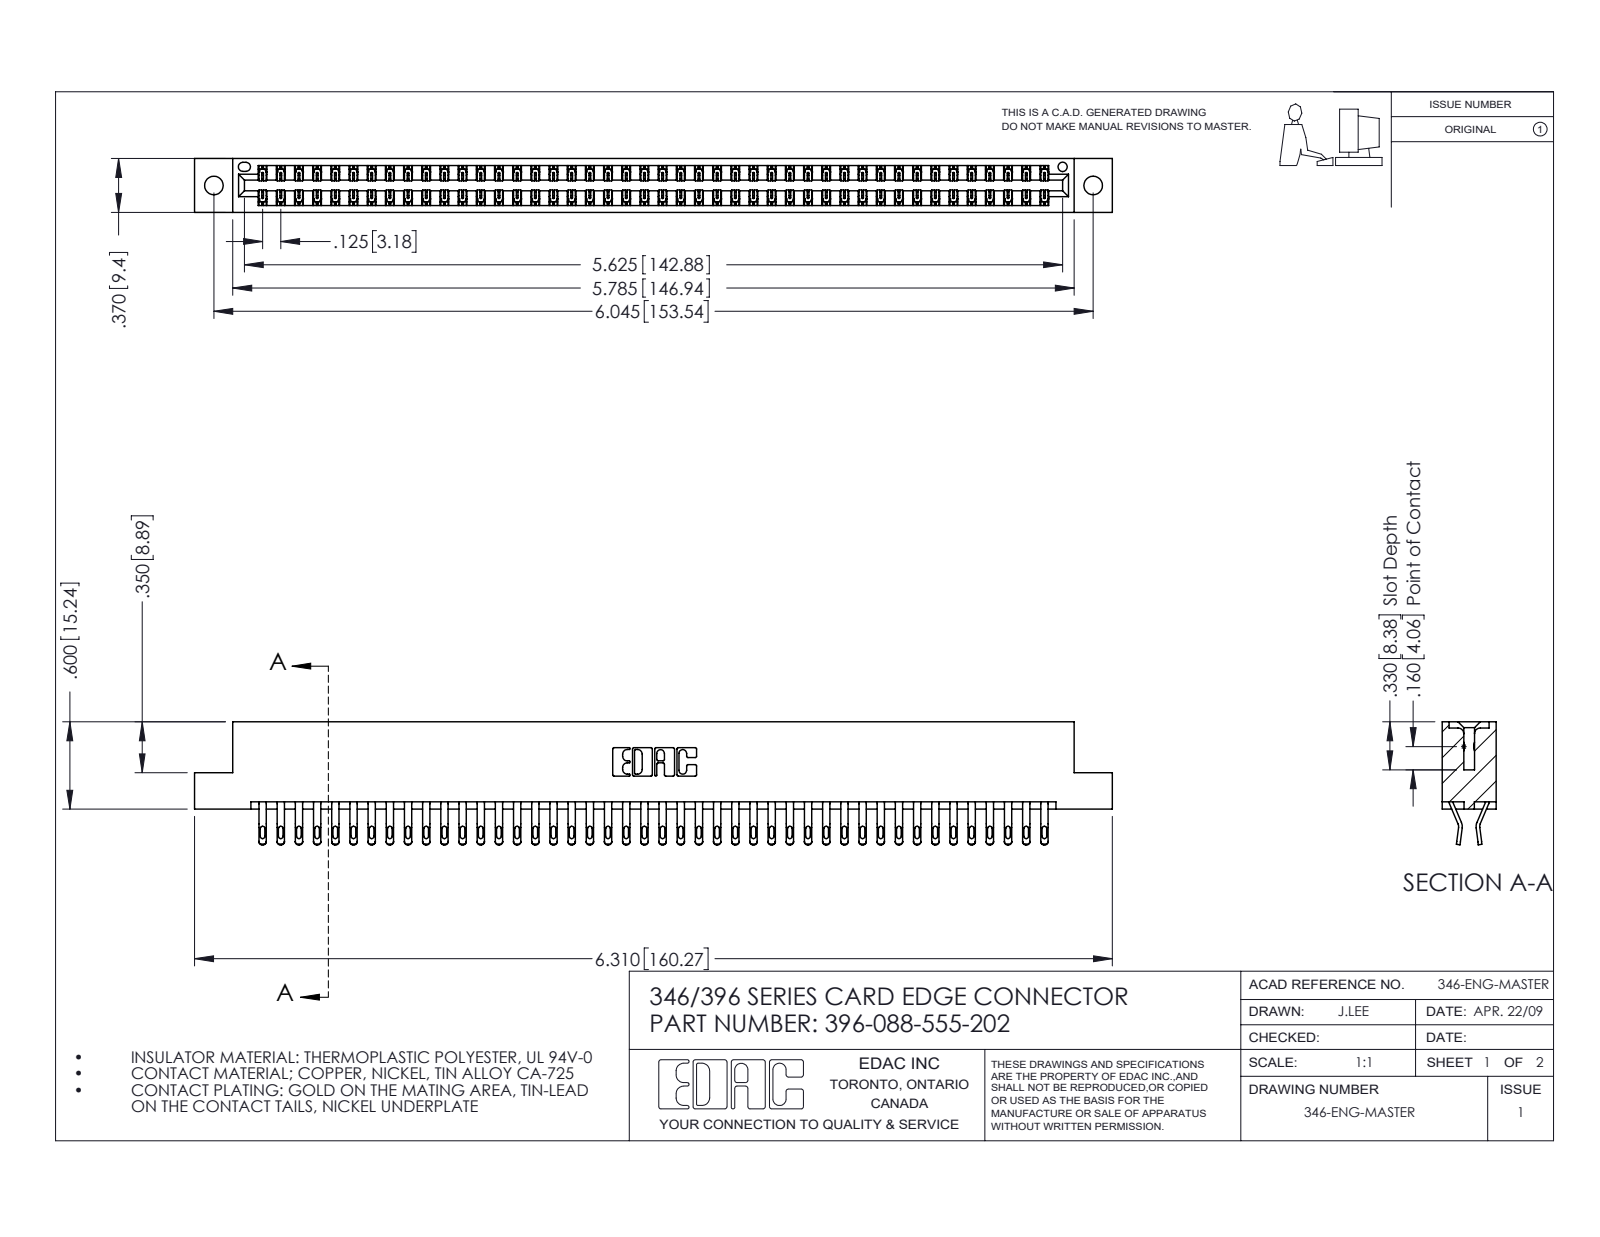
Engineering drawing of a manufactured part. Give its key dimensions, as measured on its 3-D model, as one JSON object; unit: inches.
{"part_name": "396-088-555-202; 345-292-001_555 Tail; 346 Part_Flush Mounting Lugs - 0.128 Dia", "step_written_by": "SolidWorks 2016 (CONFIG_CONTROL_DESIGN)", "units": "inches", "bodies": {"solids": 89, "faces": 5226, "planar": 2980, "cylindrical": 2246, "other": 0}, "overall_size": [6.31, 0.845, 0.37], "volume_in3": 0.968, "surface_area_in2": 34.84, "round_holes": [[0.128, 2], [0.064, 1]], "partial_cylinders_radius": [[0.016, 176], [0.02, 176], [0.006, 132], [0.01, 22], [0.007, 6], [0.031, 6], [0.026, 3], [0.01, 2]], "face_to_face_distances": [0.048, 0.322, 0.37, 0.25, 0.025, 0.072, 0.298, 0.275, 0.148, 0.222], "hole_center_spacings": [0.246, 5.836, 6.045]}
